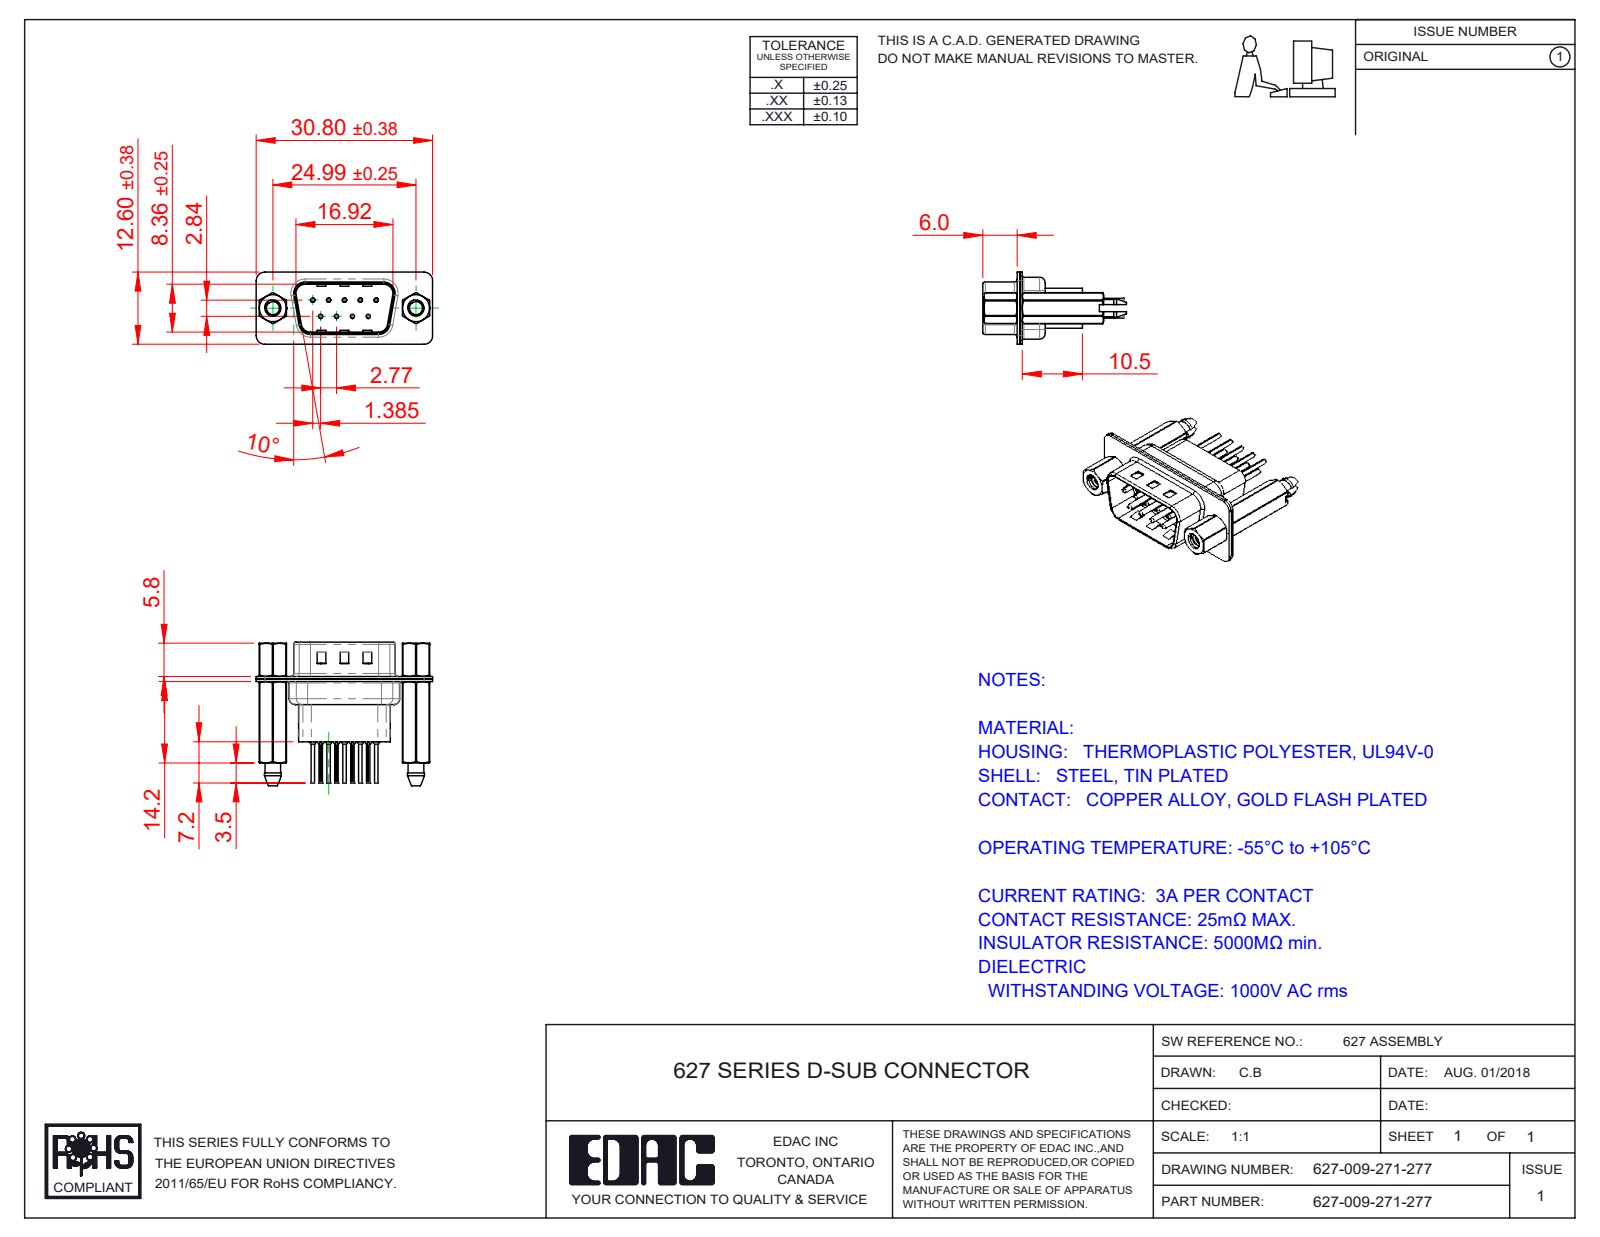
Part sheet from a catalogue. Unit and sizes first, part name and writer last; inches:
Units: inches
Overall size (bounding box): 1.213 × 0.988 × 0.496
Round holes (diameter × count): ⌀0.008 ×9, ⌀0.014 ×9, ⌀0.043 ×9, ⌀0.063 ×9, ⌀0.089 ×2, ⌀0.09 ×2, ⌀0.157 ×2, ⌀0.189 ×2
Round bosses / shafts (diameter × count): ⌀0.079 ×9, ⌀0.059 ×9, ⌀0.03 ×9, ⌀0.024 ×9, ⌀0.193 ×2, ⌀0.11 ×2
Partial cylindrical surfaces — rounded edges, fillets, slot ends (radius × count): R0.059 ×20, R0.004 ×18, R0.079 ×12, R0.063 ×10, R0.02 ×8, R0.01 ×4, R0.024 ×4, R0.026 ×4
Main face-to-face distances: 0.018, 0.016, 0.035, 0.187, 0.032, 0.377, 0.055, 0.059, 0.027, 0.302
Hole centre spacings: 0.124, 0.109, 0.218, 0.198, 0.198, 0.327, 0.294, 0.295
Volume: 0.143 in³ · Surface area: 9.334 in²
Bodies: 16 solids, 1420 faces (377 planar, 600 cylindrical, 443 other)
Part name (STEP PRODUCT): 627 Housing_09 HP; 627 4-40 Hex Standoff; 627 Contact Row 2_61; 627 4-40 Threaded Boardlock_HP71 (+4 more)
STEP written by: SolidWorks 2020 (CONFIG_CONTROL_DESIGN)
